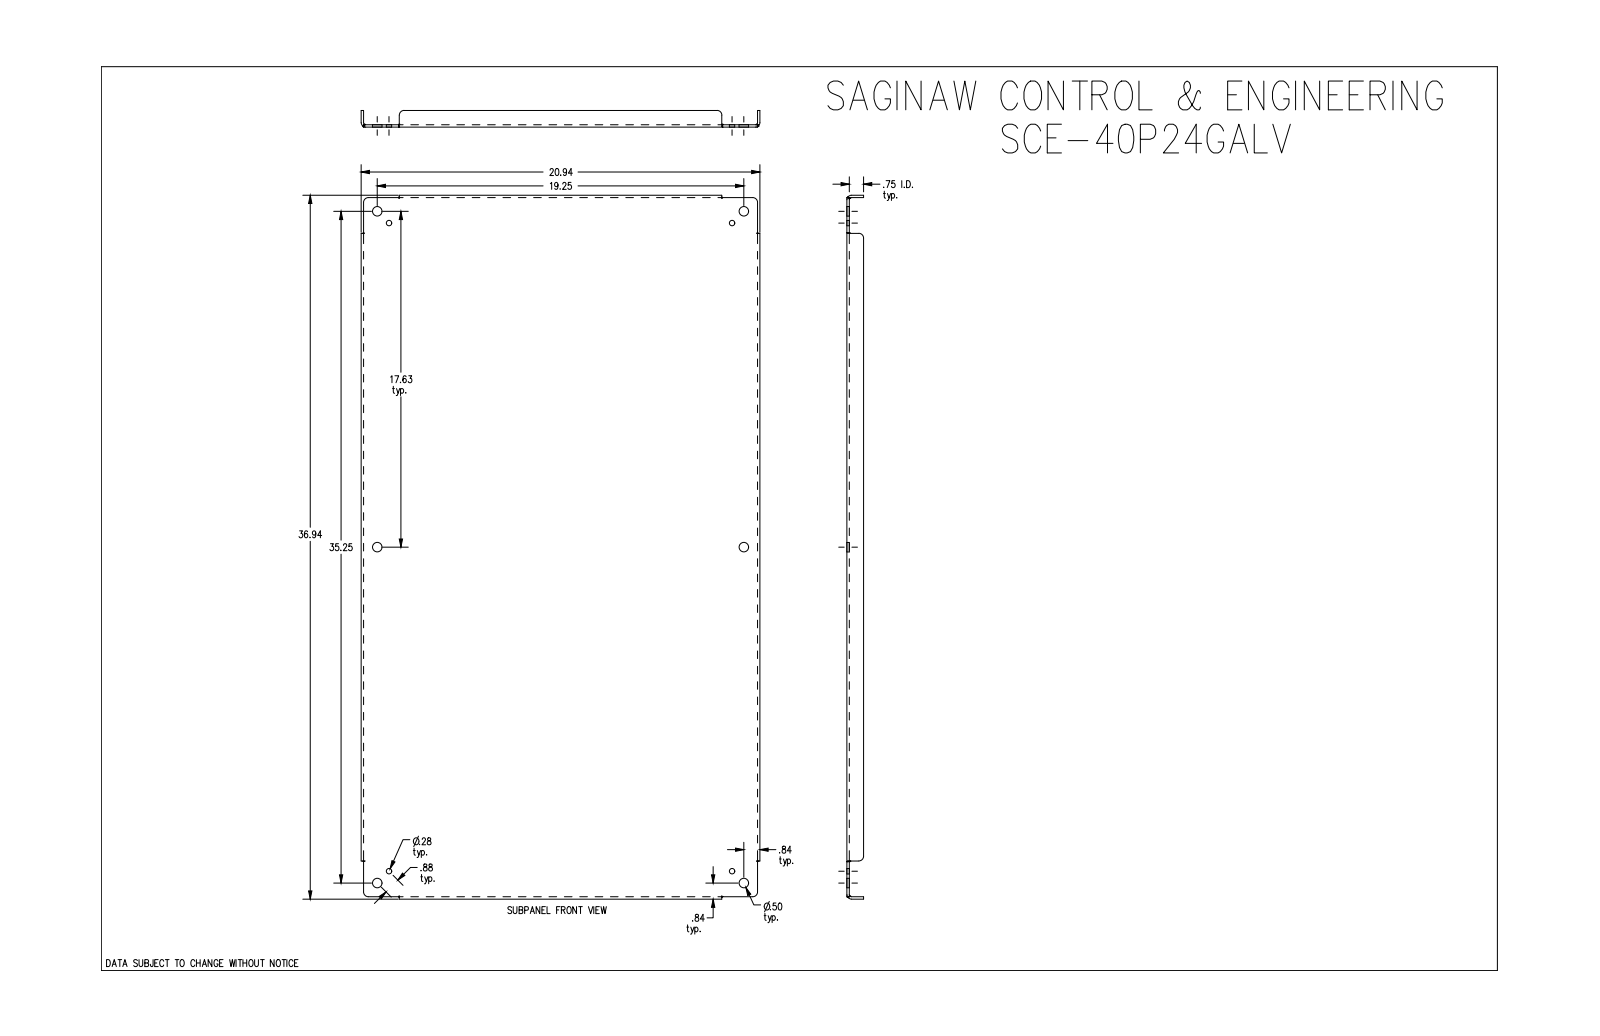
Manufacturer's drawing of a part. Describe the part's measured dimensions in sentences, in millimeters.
The part is named "SCE-40P24GALV". Its 3-D file was written by "SolidWorks 2019 (CONFIG_CONTROL_DESIGN)". It is 1 solid with 84 faces: 30 planar, 30 cylindrical and 24 other. Overall it measures 938.2 by 531.8 by 22.2 millimeters. Its volume is 1 714 000 cubic millimeters and its surface area 1 091 000 square millimeters. Round holes: 6 of diameter 12.7, 4 of diameter 7.1. Partial cylindrical surfaces (rounded edges, fillets, slot ends): 8 of radius 6.4, 4 of radius 2.8, 4 of radius 6. The main face-to-face distances are 3.2, 3.2, 528.7, 935.1, 525.4, 531.8, 19.1, 22.2, 931.8, 938.2. The hole center spacings are 22.2, 432.3, 447.7, 473.5, 640.7, 662.9, 879.8, 998.9.
